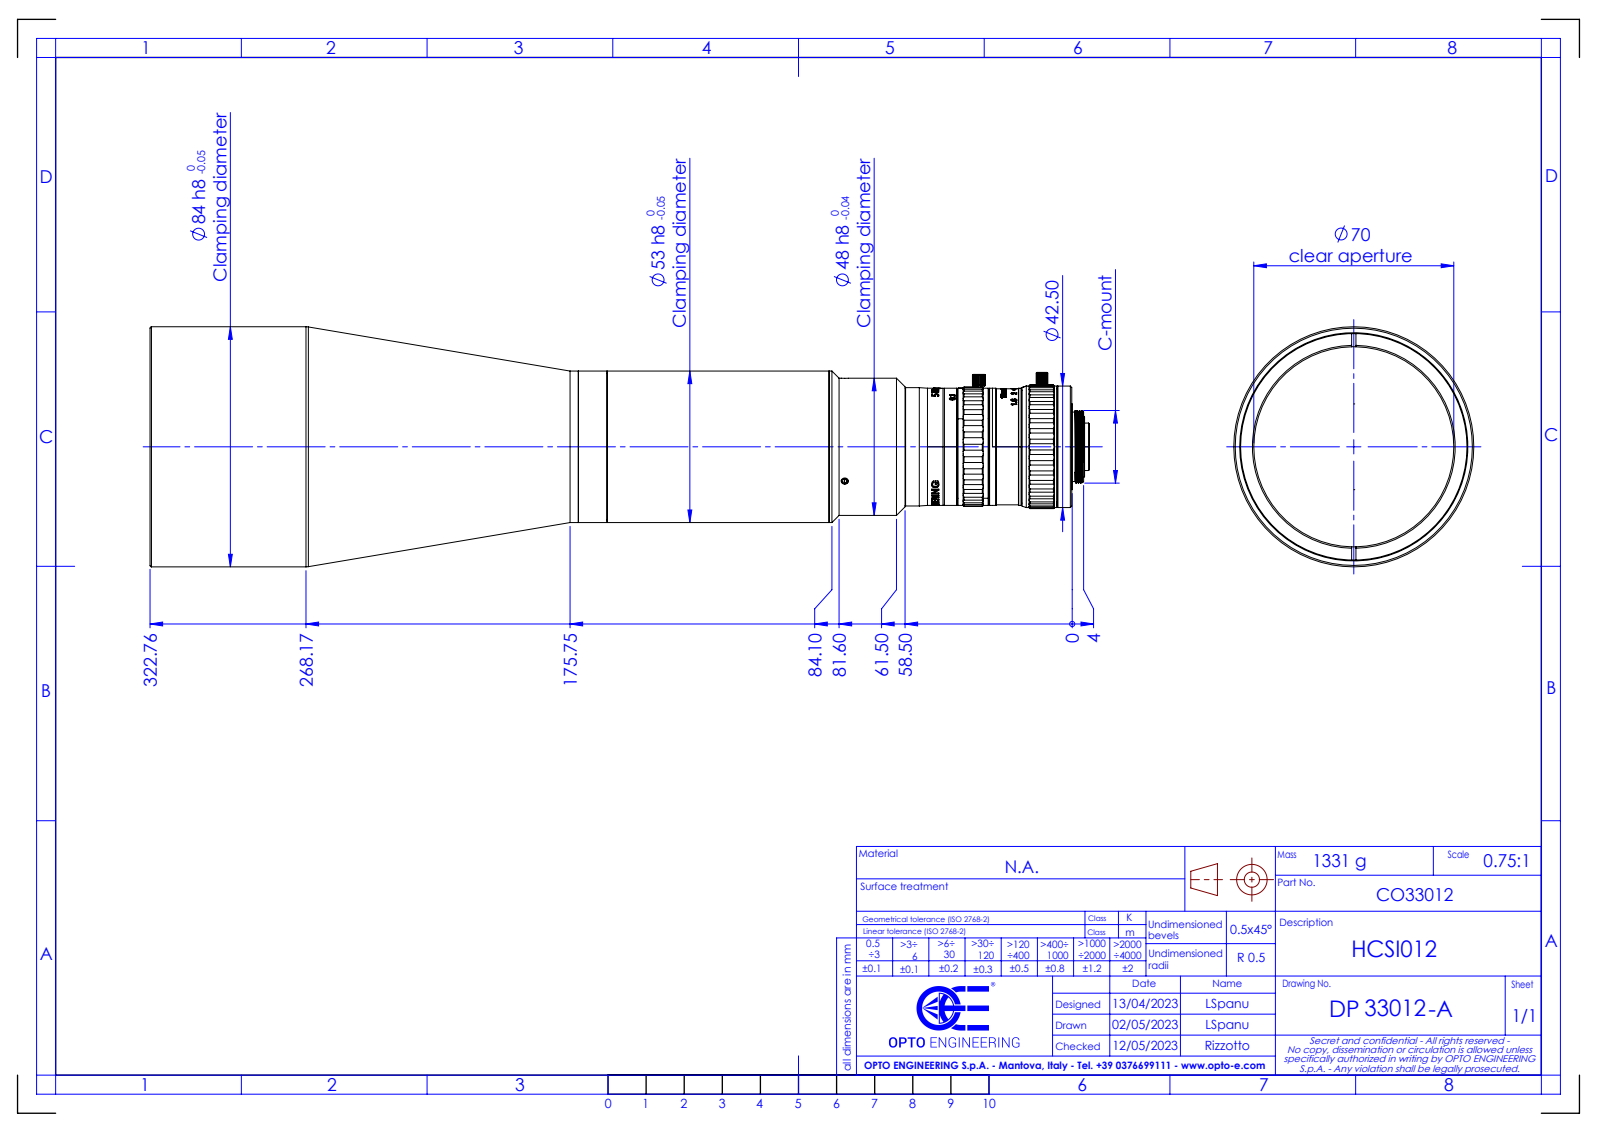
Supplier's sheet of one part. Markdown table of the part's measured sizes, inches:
| quantity | value |
| --- | --- |
| part name | DP33012-A_HCSI012 |
| STEP written by | SolidWorks 2021 (CONFIG_CONTROL_DESIGN) |
| units | inches |
| bodies | 0 solids, 611 faces (107 planar, 312 cylindrical, 192 other) |
| overall size | 12.945 × 3.307 × 3.307 |
| round holes (diameter × count) | 0.098 × 2, 0.102 × 2, 0.512 × 1, 1.189 × 1, 2.756 × 1, 3.12 × 1 |
| round bosses / shafts (diameter × count) | 3.307 × 1, 2.087 × 1, 1.89 × 1, 1.673 × 1, 1.63 × 1, 1.614 × 1, 1.61 × 1, 1.598 × 1 |
| partial cylindrical surfaces (radius × count) | 0.079 × 67, 0.039 × 1, 0.089 × 1, 0.798 × 1, 0.802 × 1, 0.803 × 1, 0.807 × 1, 0.823 × 1 |
| main face-to-face distances | 0.108, 9.337, 9.228, 12.681, 12.573, 3.344, 0.02, 0.128, 9.357, 12.701 |
| hole center spacings | 0.689, 1.194 |
